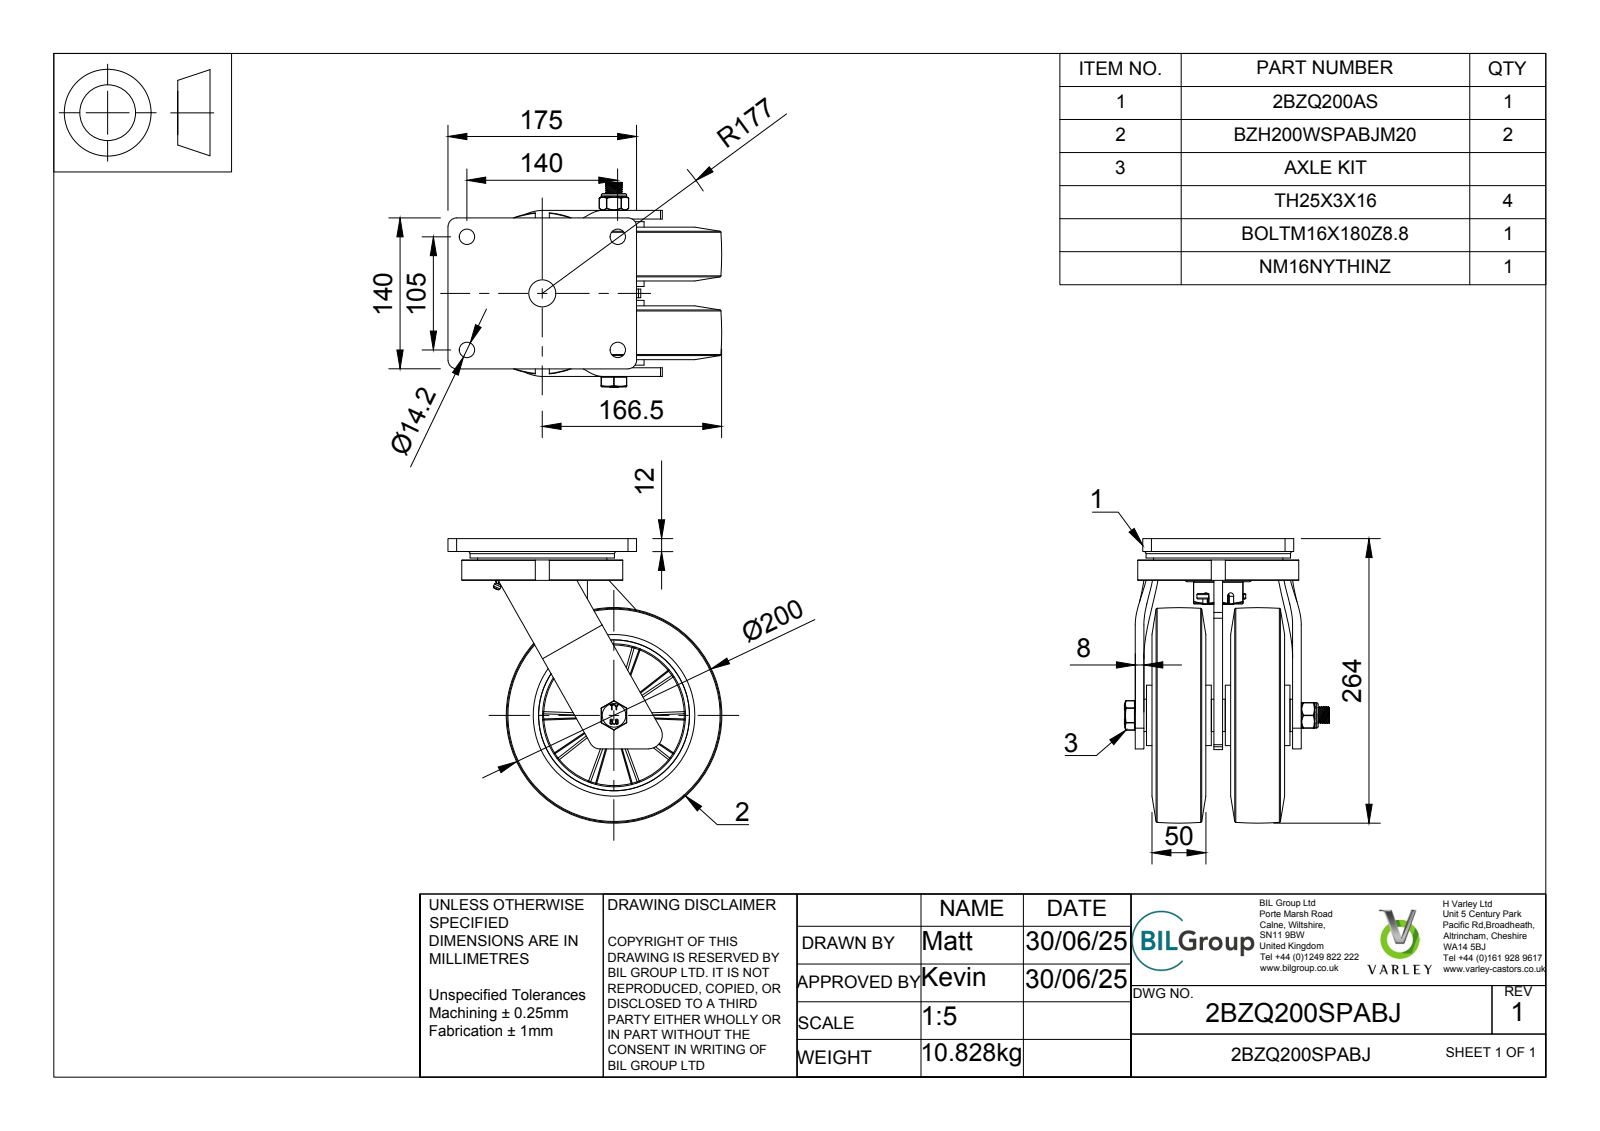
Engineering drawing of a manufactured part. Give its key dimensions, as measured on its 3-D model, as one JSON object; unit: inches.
{"part_name": "2BZQ200SPABJ v4; 2BZQ200AS v1; FABRICATED STEEL TOP PLATE; TOP PLATE (+8 more)", "step_written_by": "Autodesk Translation Framework v14.10.0.0 (AUTOMOTIVE_DESIGN)", "units": "inches", "bodies": {"solids": 70, "faces": 2589, "planar": 794, "cylindrical": 411, "other": 1384}, "overall_size": [10.394, 10, 7.482], "volume_in3": 179.5, "surface_area_in2": 1057, "round_holes": [[0.559, 4], [0.236, 1], [0.63, 1], [0.638, 1], [0.64, 1], [0.709, 1], [0.787, 1], [0.984, 1], [1.122, 1], [1.181, 1], [1.213, 1], [1.587, 1]], "round_bosses_or_shafts": [[1.063, 2], [5.906, 1], [5.276, 1], [4.724, 1], [2.205, 1], [1.606, 1], [1.232, 1], [1.181, 1]], "partial_cylinders_radius": [[0.02, 47], [0.035, 20], [0.315, 5], [0.026, 4], [0.039, 4], [0.05, 4], [0.128, 3], [0.138, 3]], "face_to_face_distances": [2.874, 0.472, 2.303, 0.315, 1.614, 1.909, 0.276, 0.61, 0.079, 0.965], "hole_center_spacings": [3.445, 4.134, 5.512, 6.89]}
